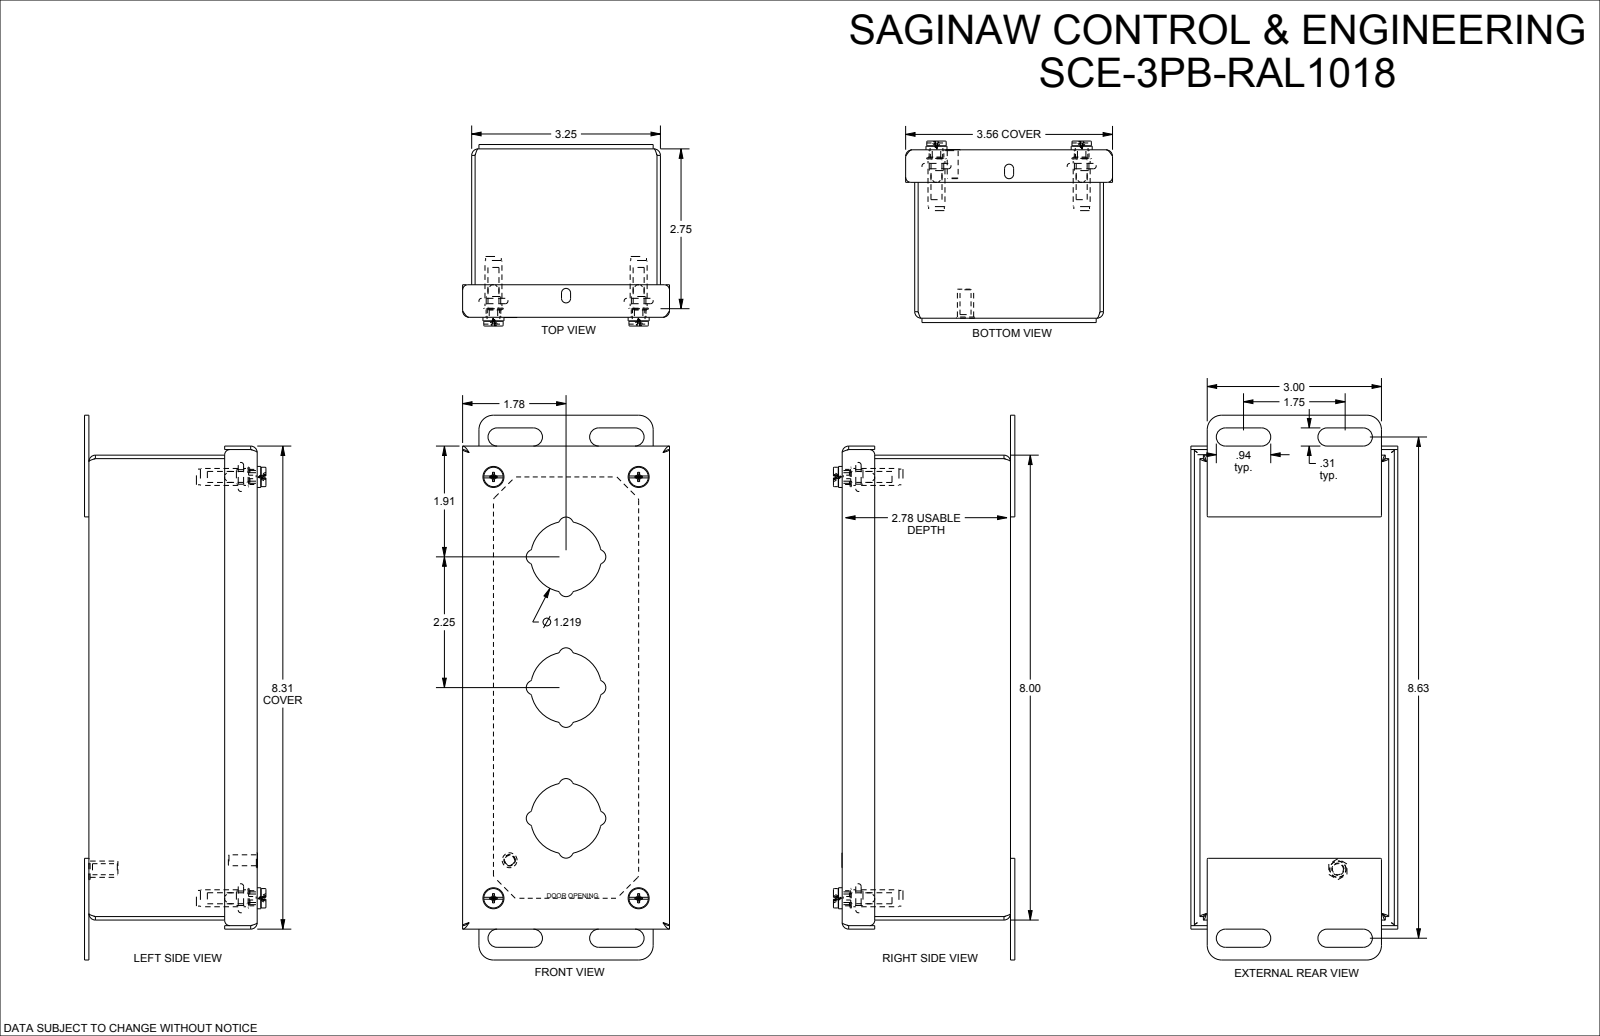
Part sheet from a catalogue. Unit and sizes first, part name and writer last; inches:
Units: inches
Overall size (bounding box): 9.375 × 3.563 × 3.124
Round holes (diameter × count): ⌀0.19 ×5, ⌀0.22 ×4, ⌀0.25 ×4, ⌀0.266 ×4, ⌀0.317 ×4
Round bosses / shafts (diameter × count): ⌀0.188 ×5, ⌀0.437 ×4, ⌀0.362 ×4, ⌀0.34 ×4, ⌀0.334 ×4, ⌀0.292 ×4, ⌀0.27 ×4, ⌀0.26 ×4
Partial cylindrical surfaces — rounded edges, fillets, slot ends (radius × count): R0.04 ×24, R0.06 ×20, R0.125 ×12, R0.015 ×8, R0.063 ×8, R0.115 ×8, R0.156 ×8, R0.245 ×8
Main face-to-face distances: 0.06, 2.838, 3.19, 2.778, 2.898, 3.25, 3.13, 0.156, 7.94, 3.346
Hole centre spacings: 2.5, 2.5, 7.25, 7.669, 7.247, 7.25, 7.669, 2.061
Volume: 9.235 in³ · Surface area: 307.5 in²
Bodies: 19 solids, 583 faces (209 planar, 204 cylindrical, 170 other)
Part name (STEP PRODUCT): SCE-3PB-RAL1018
STEP written by: SolidWorks 2021 (AUTOMOTIVE_DESIGN)
